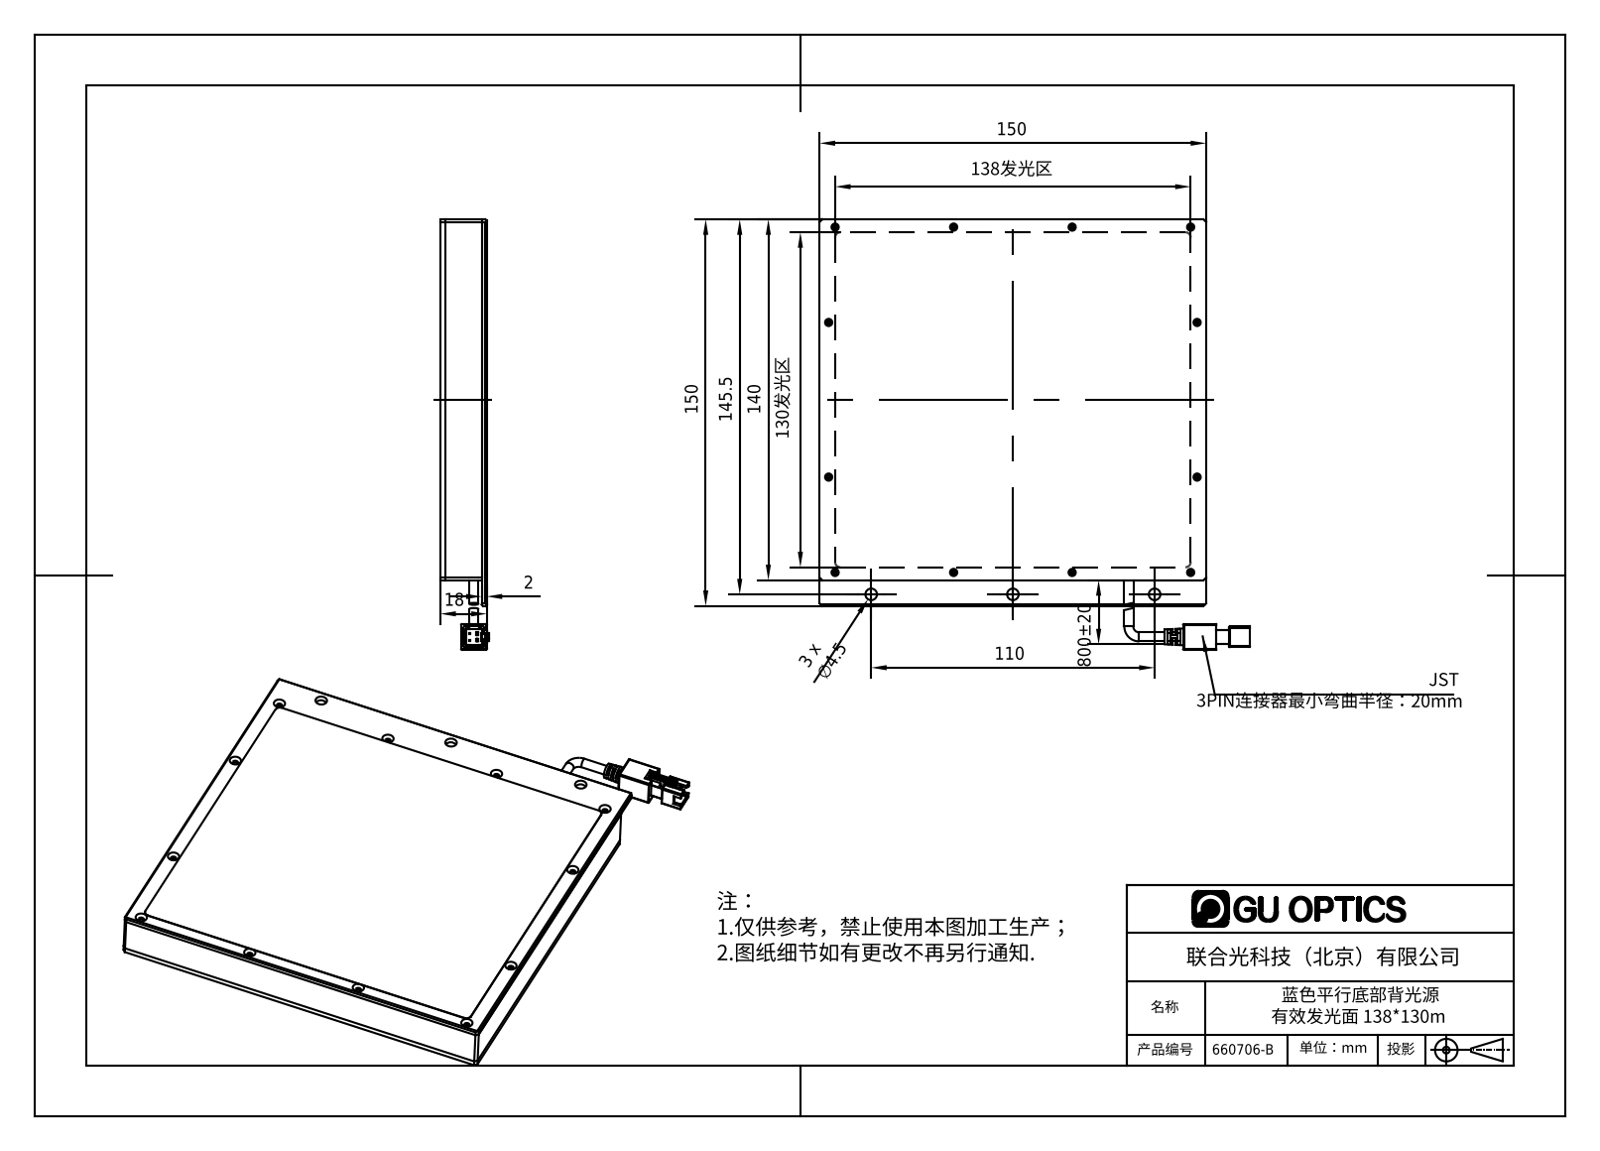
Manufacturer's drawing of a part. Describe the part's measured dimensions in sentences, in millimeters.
The part is named "660706-B". Its 3-D file was written by "SolidWorks 2016 (AUTOMOTIVE_DESIGN)". It is 22 solids with 3025 faces: 2614 planar, 253 cylindrical and 158 other. Overall it measures 167 by 167 by 18.7 millimeters. Its volume is 172 695 cubic millimeters and its surface area 157 551 square millimeters. Round holes: 12 of diameter 1.1, 12 of diameter 1.4, 12 of diameter 1.5, 12 of diameter 1.6, 12 of diameter 2, 12 of diameter 2.2, 12 of diameter 2.8, 3 of diameter 4.5. Round bosses or shafts: 2 of diameter 3.5. Partial cylindrical surfaces (rounded edges, fillets, slot ends): 15 of radius 0.1, 13 of radius 0.2, 12 of radius 0.4, 4 of radius 1, 4 of radius 2, 2 of radius 1.5, 1 of radius 0.3, 1 of radius 0.68. The main face-to-face distances are 2, 14, 16, 2.1, 16.1, 18.1, 12, 4.1, 5, 1. The hole center spacings are 46, 141.68, 37.08, 61, 92, 97.03, 101.49, 108.45.
